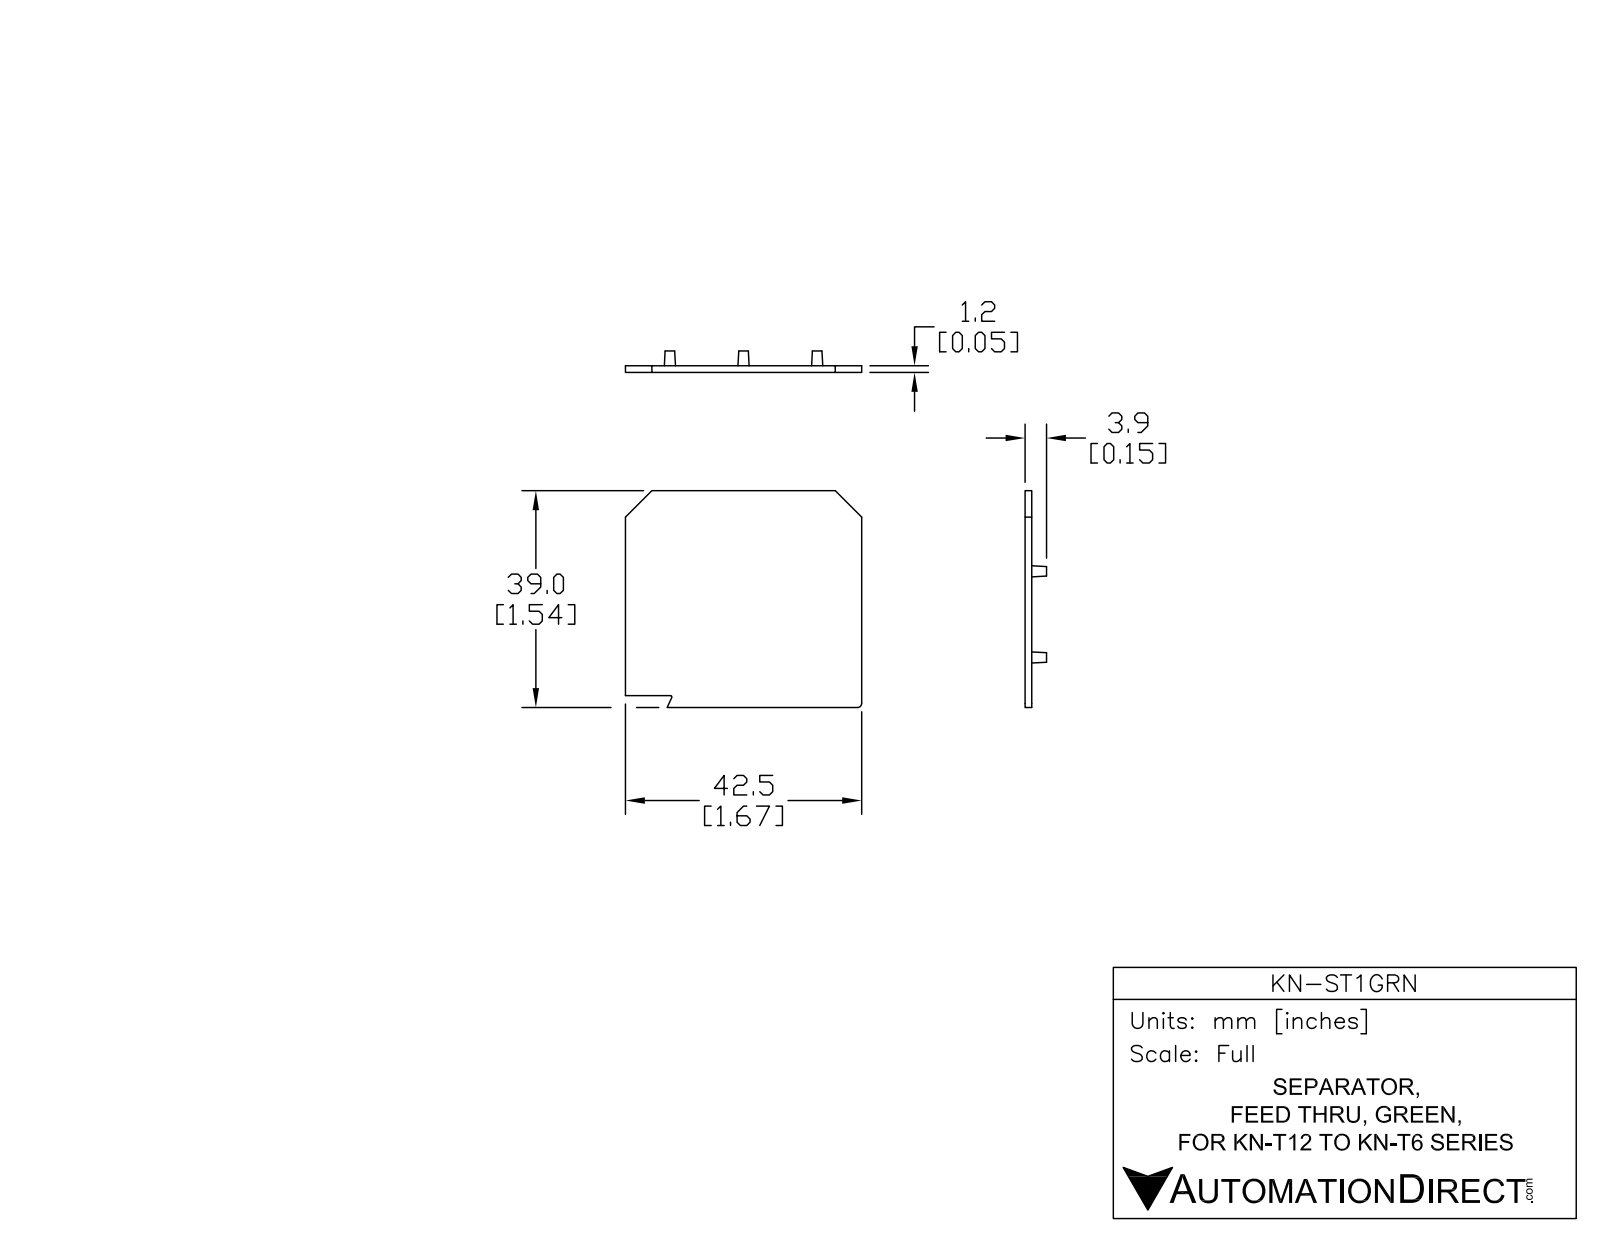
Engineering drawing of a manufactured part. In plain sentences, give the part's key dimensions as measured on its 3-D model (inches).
The part is named "KN-ST1BLU". Its 3-D file was written by "SolidWorks 2014 (AUTOMOTIVE_DESIGN)". It is 1 solid with 30 faces: 16 planar, 2 cylindrical and 12 other. Overall it measures 1.673 by 1.535 by 0.152 inches. Its volume is 0.12 cubic inches and its surface area 5.405 square inches. Partial cylindrical surfaces (rounded edges, fillets, slot ends): 1 of radius 0.01, 1 of radius 0.03. The main face-to-face distances are 0.047, 1.535, 1.673, 0.085, 1.451, 0.105, 0.152.
